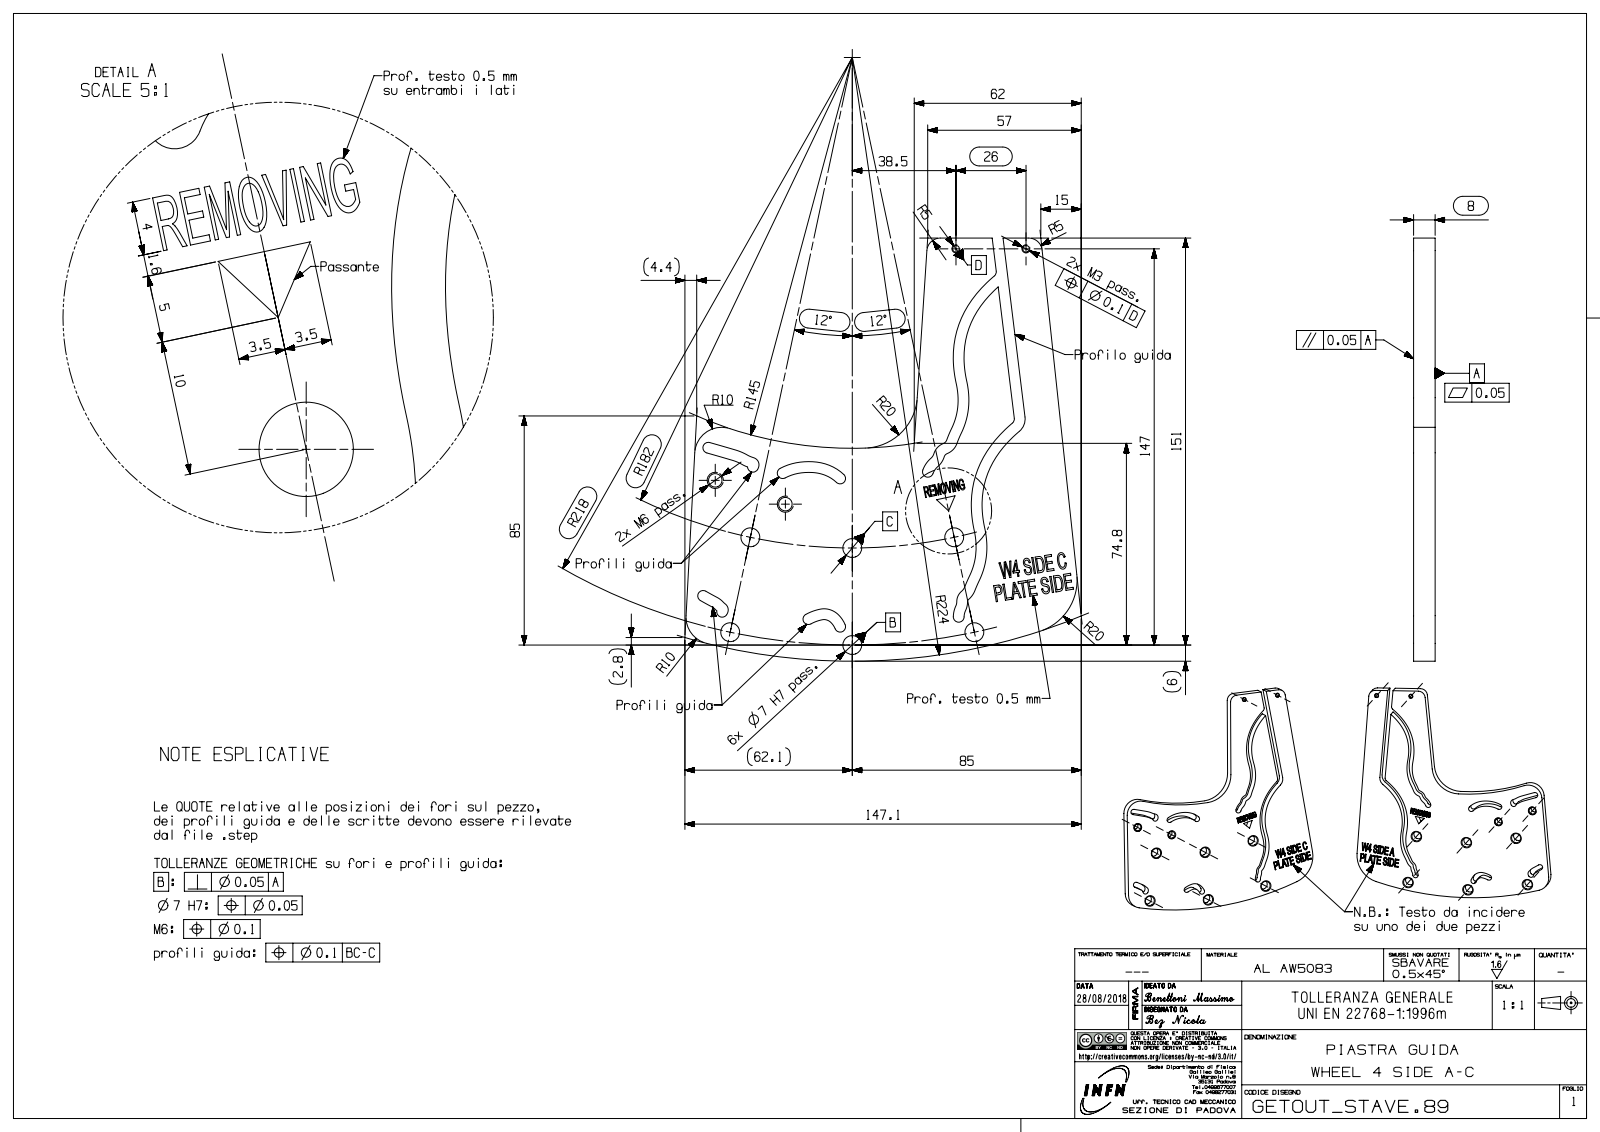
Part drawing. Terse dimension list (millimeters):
name: bez8324385A6ux3
written by: SIEMENS PLM Software NX 12.0 (AUTOMOTIVE_DESIGN)
unit: mm
bodies: 1 solid, 550 faces (401 planar, 31 cylindrical, 118 other)
size: 173.44 × 149.74 × 8
volume: 104 741 mm³; area: 37 848 mm²
holes: 6× ⌀7, 2× ⌀2.5, 2× ⌀5
rounds: 12× R2, 2× R5, 2× R10, 2× R20, 1× R6, 1× R145, 1× R224
face distances: 8, 4.02, 0.5, 7.5, 7, 4.01, 5.29, 0.49, 3.45, 0.47
hole spacings: 36, 55.04, 55.05, 90.31, 17.91, 24.83, 26, 27.5
